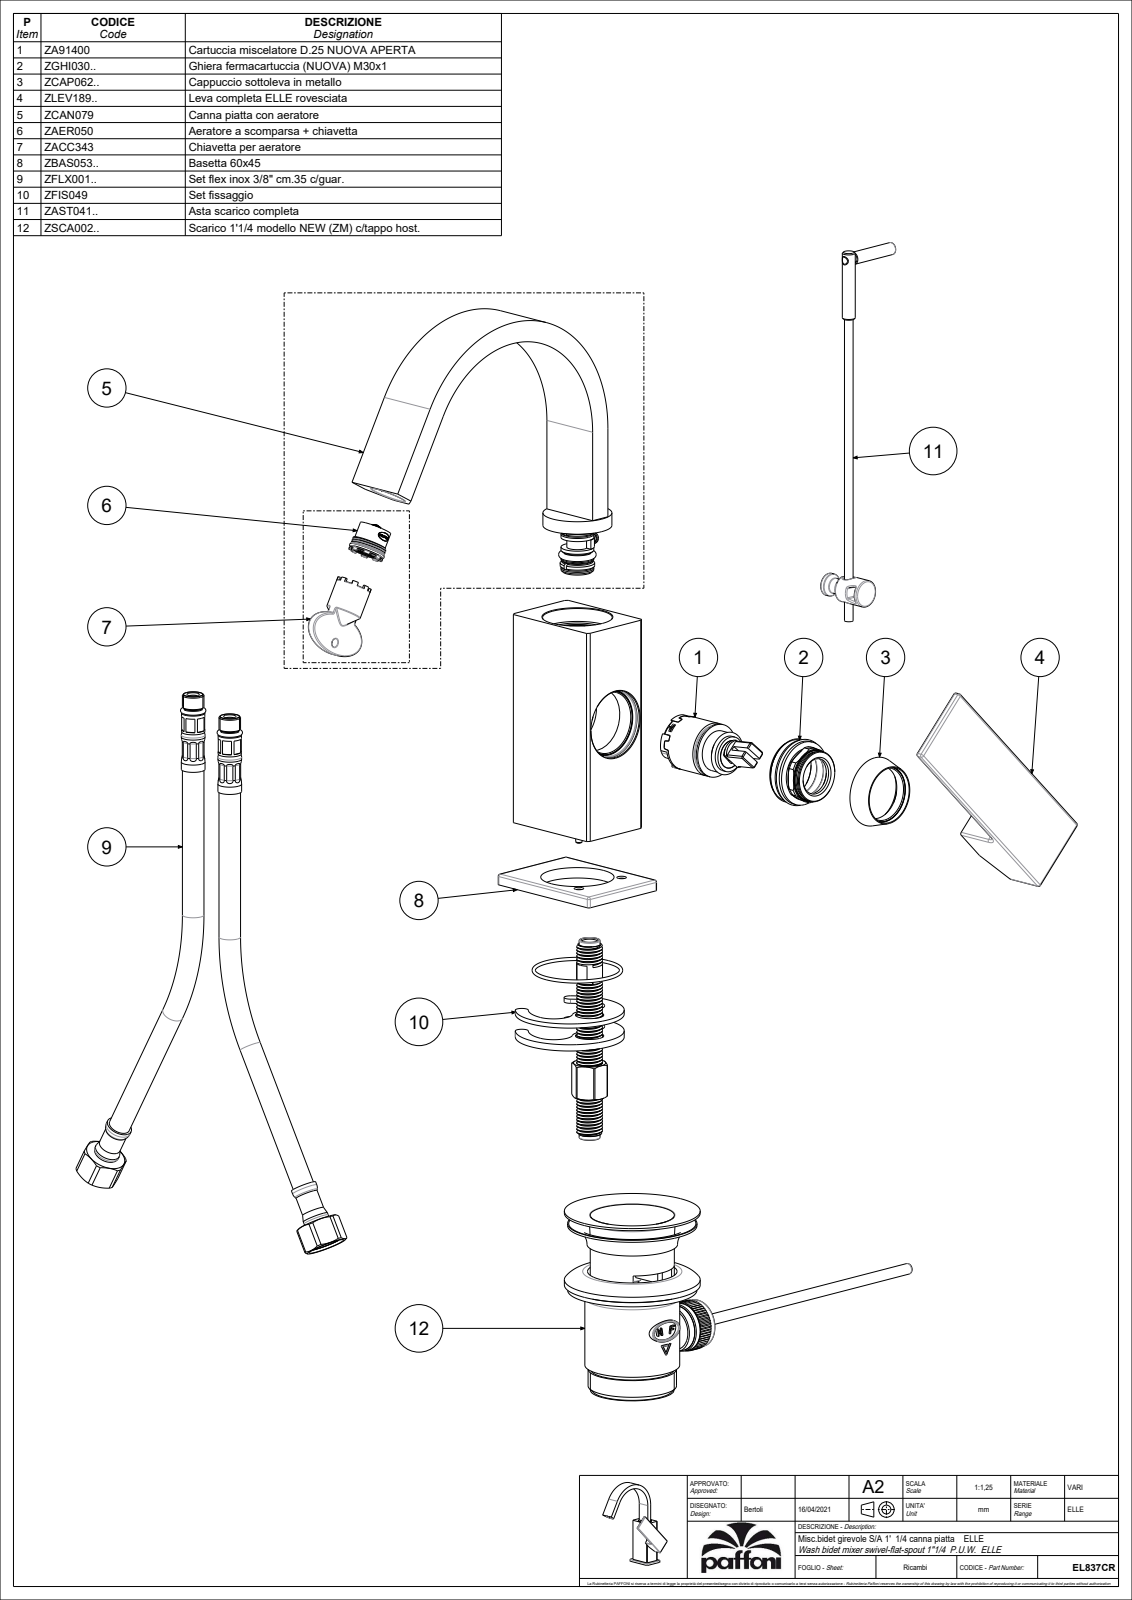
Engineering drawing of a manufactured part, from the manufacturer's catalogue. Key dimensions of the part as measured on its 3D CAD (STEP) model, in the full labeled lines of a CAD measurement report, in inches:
Part name (STEP PRODUCT): EL837CR
STEP written by: CREO PARAMETRIC BY PTC INC, 2020044 (CONFIG_CONTROL_DESIGN)
Units: inches
Bodies: 1 solid, 376 faces (120 planar, 147 cylindrical, 109 other)
Overall size (bounding box): 8.268 × 6.336 × 3.279
Volume: 15.41 in³ · Surface area: 114.7 in²
Round holes (diameter × count): ⌀0.236 ×3, ⌀0.118 ×2, ⌀0.126 ×2, ⌀0.157 ×2, ⌀0.197 ×2, ⌀0.217 ×2, ⌀0.354 ×2, ⌀0.433 ×2, ⌀0.13 ×1, ⌀0.177 ×1, ⌀0.276 ×1, ⌀0.315 ×1
Round bosses / shafts (diameter × count): ⌀1.528 ×1, ⌀0.787 ×1, ⌀0.346 ×1, ⌀0.299 ×1, ⌀0.224 ×1, ⌀0.197 ×1, ⌀0.157 ×1
Partial cylindrical surfaces — rounded edges, fillets, slot ends (radius × count): R0.039 ×21, R0.059 ×8, R0.118 ×2, R0.138 ×1, R0.197 ×1, R0.232 ×1, R0.252 ×1, R1.181 ×1
Main face-to-face distances: 0.394, 1.417, 1.575, 3.082, 0.906, 0.512, 0.157, 1.181, 1.113, 1.507
Hole centre spacings: 0.265, 0.352, 0.368, 0.371, 0.445, 0.601, 0.609, 0.118
